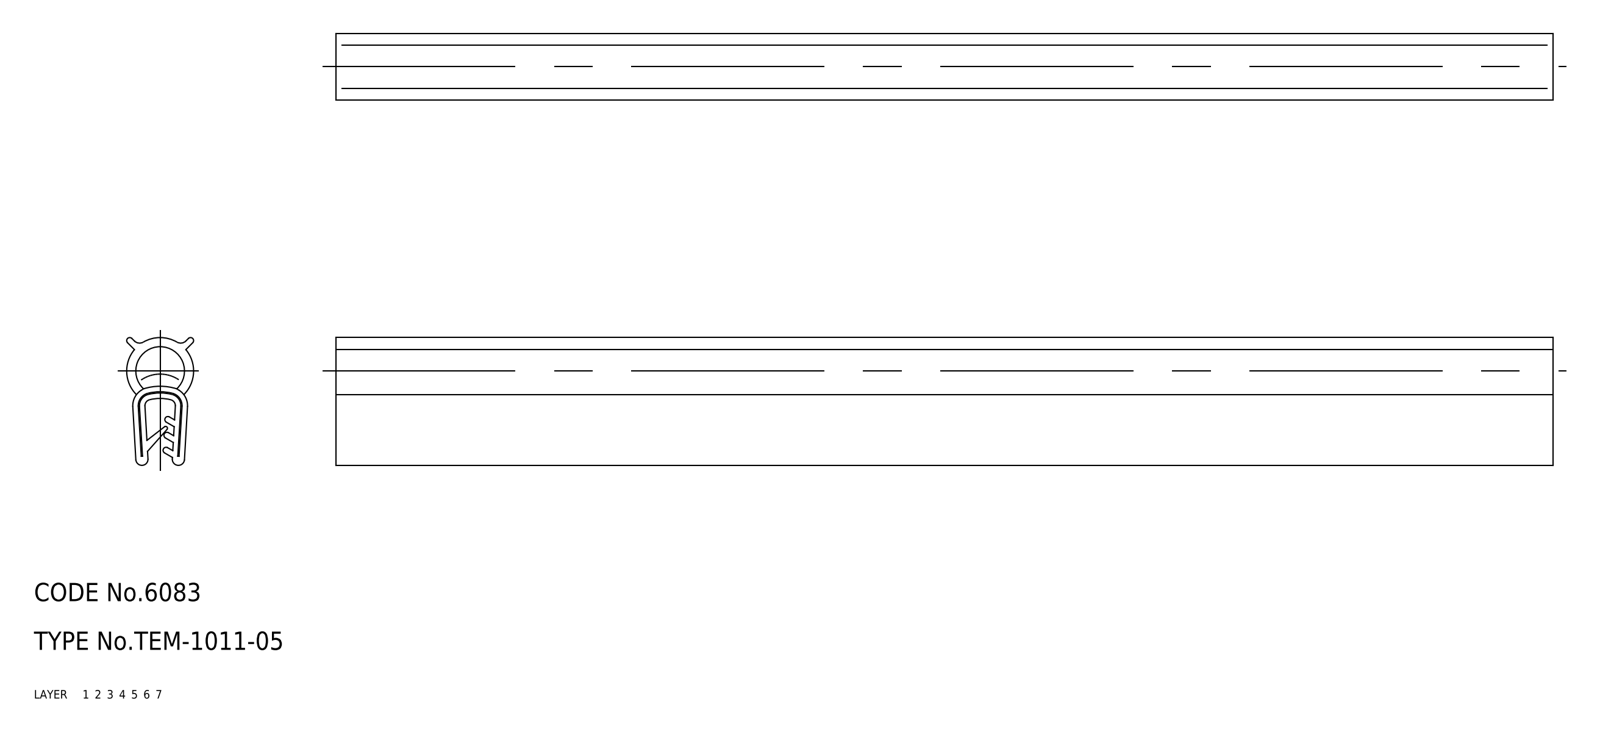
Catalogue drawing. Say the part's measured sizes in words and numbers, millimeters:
The part is named "rubber foam; gasket; center core; TEM_1011_05_29880_36". Its 3-D file was written by "CADfix (AUTOMOTIVE_DESIGN)". It is 3 solids with 76 faces: 0 planar, 0 cylindrical and 76 other. Overall it measures 200 by 21 by 11 millimeters. Its volume is 20 832 cubic millimeters and its surface area 47 431 square millimeters.
